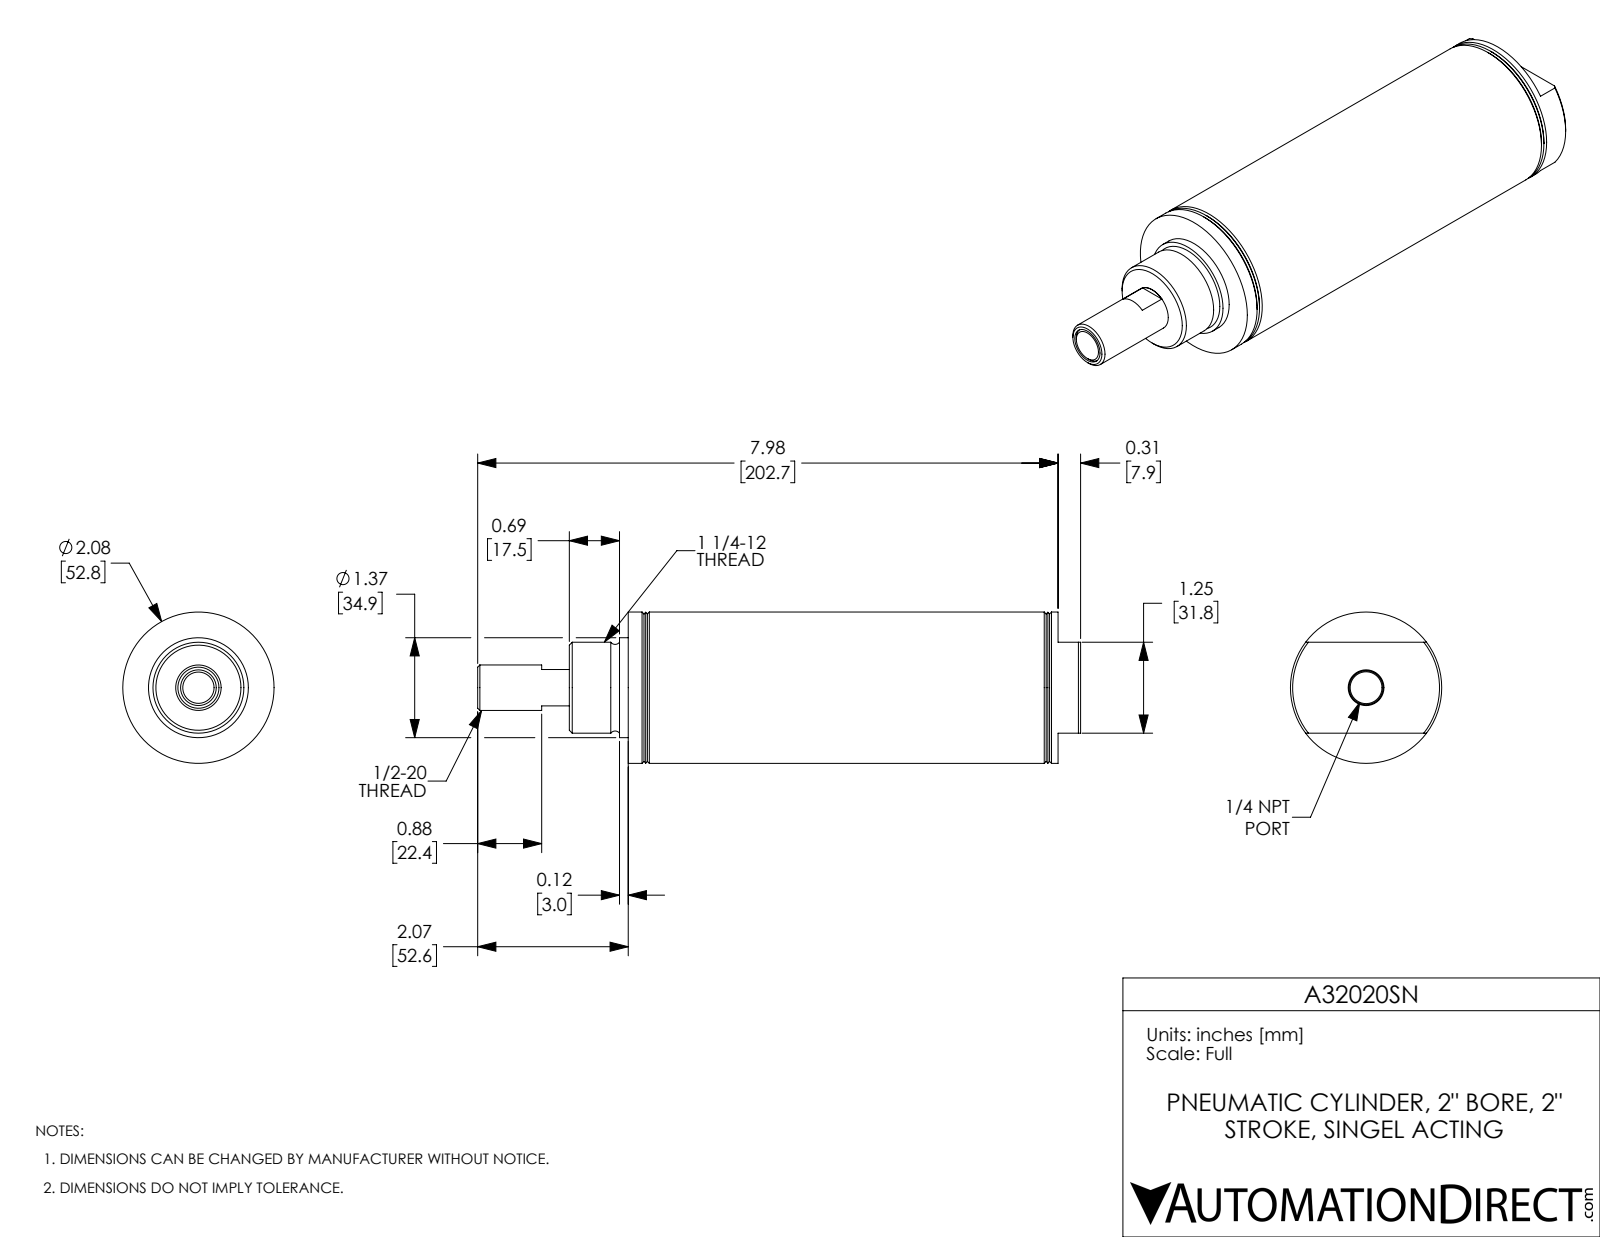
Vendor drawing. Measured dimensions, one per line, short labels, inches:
name: A32020SN-MainBody; A32020SN-Rod; A32020SN
written by: SolidWorks 2017 (AUTOMOTIVE_DESIGN)
unit: in
bodies: 2 solids, 76 faces (21 planar, 22 cylindrical, 33 other)
size: 8.29 × 2.08 × 2.08
volume: 16.41 in³; area: 99.68 in²
holes: 1× ⌀0.438, 1× ⌀0.491, 1× ⌀0.625, 1× ⌀2
bosses: 1× ⌀2.08, 1× ⌀1.373, 1× ⌀1.25
face distances: 1.86, 4.36, 0.5, 2.5, 2, 2.36, 6.22, 3.86, 0.31, 1.55
